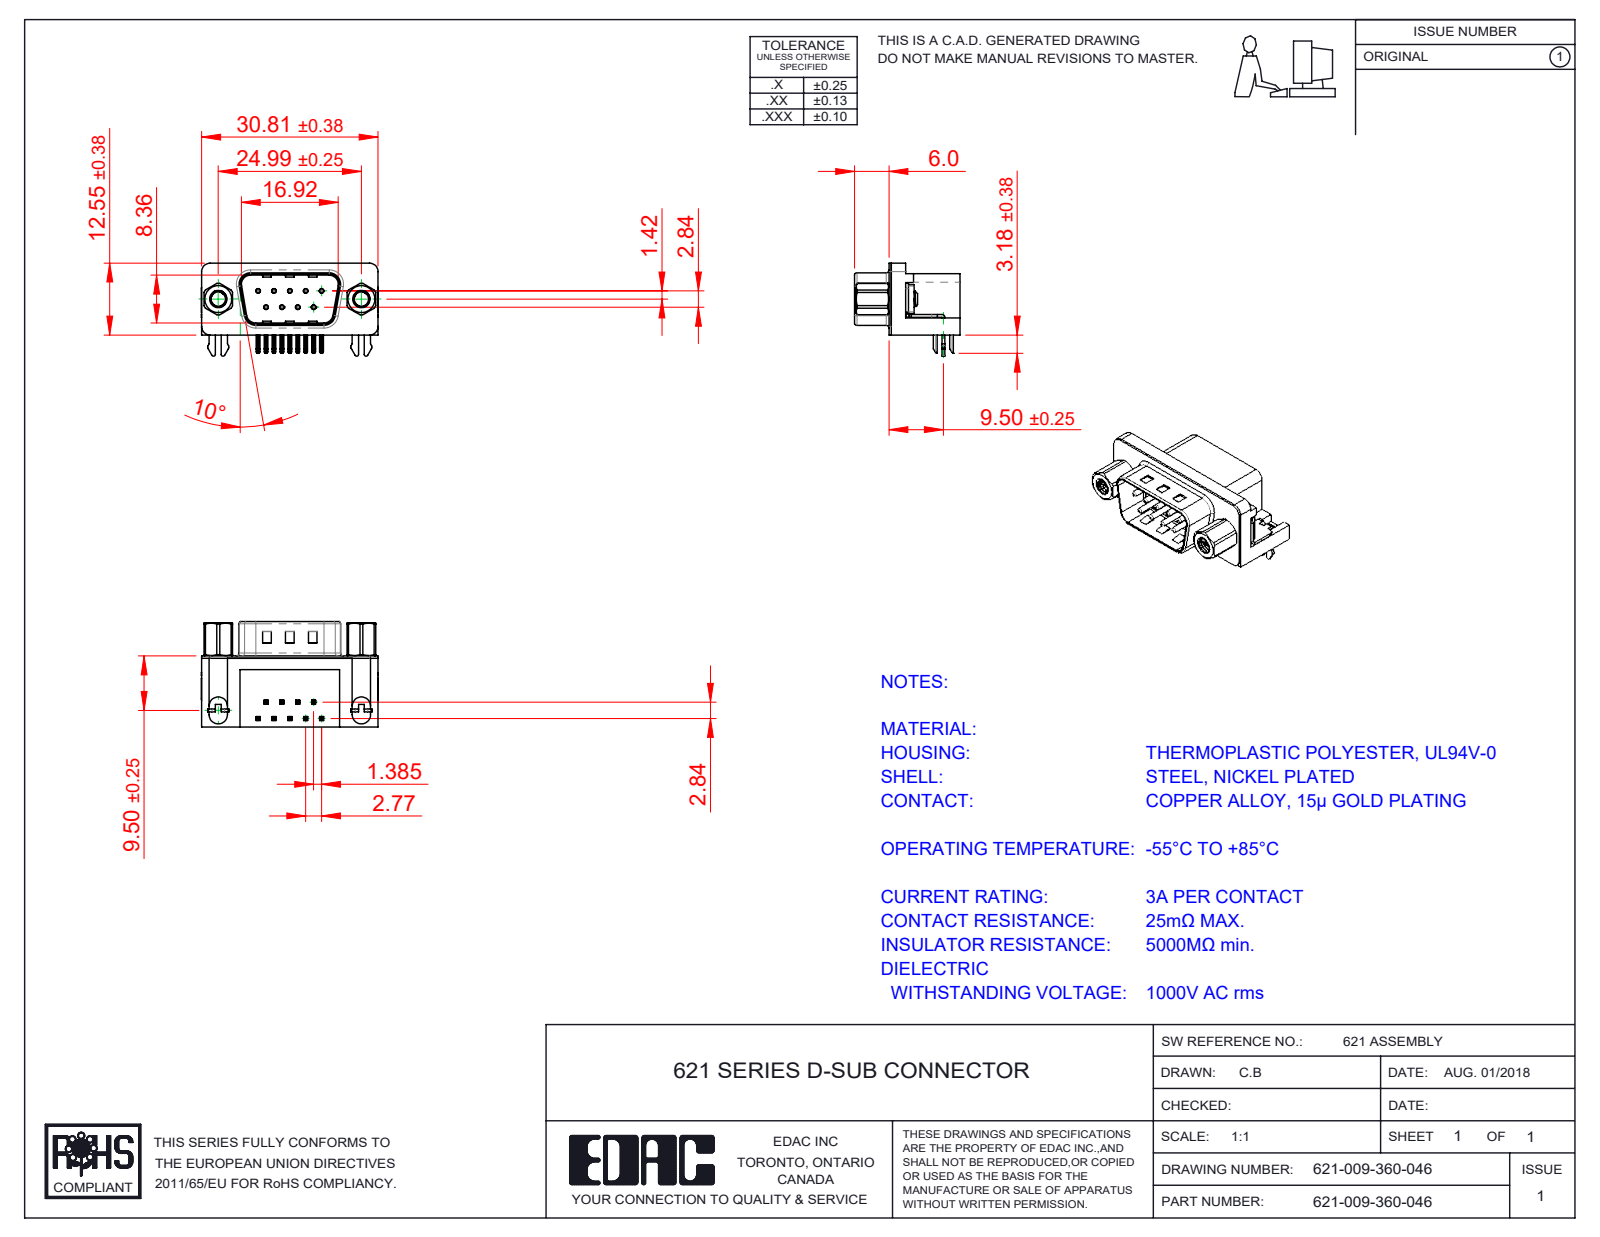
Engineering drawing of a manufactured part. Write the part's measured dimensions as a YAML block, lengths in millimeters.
part_name: "621 4 Prong Board Lock; 621 Housing_9 Socket; 621 Shell_9 Socket; 621-009-360-046 (+4 more)"
step_written_by: "SolidWorks 2016 (CONFIG_CONTROL_DESIGN)"
units: millimeters
bodies: {solids: 17, faces: 1259, planar: 637, cylindrical: 417, other: 205}
overall_size: [30.89, 18.4, 16.25]
volume: 3495
surface_area: 5028
round_holes:
  - {diameter: 0.35, count: 9}
  - {diameter: 0.8, count: 9}
  - {diameter: 2, count: 2}
  - {diameter: 2.5, count: 2}
  - {diameter: 4, count: 2}
  - {diameter: 4.8, count: 2}
  - {diameter: 5, count: 2}
round_bosses_or_shafts:
  - {diameter: 0.75, count: 9}
  - {diameter: 3, count: 4}
  - {diameter: 4.9, count: 2}
  - {diameter: 4.75, count: 2}
  - {diameter: 3.9, count: 2}
partial_cylinders:
  - {radius: 0.25, count: 48}
  - {radius: 0.12, count: 18}
  - {radius: 1, count: 16}
  - {radius: 0.5, count: 9}
  - {radius: 1.5, count: 8}
  - {radius: 1.6, count: 8}
  - {radius: 0.9, count: 4}
  - {radius: 2, count: 4}
face_to_face_distances: [0.4, 12, 12.4, 10.35, 9.5, 2.5, 2.9, 2.1, 0.35, 10.7]
hole_center_spacings: [3.16, 2.77, 5.54, 5.03, 5.04, 8.31, 7.48, 7.49]
